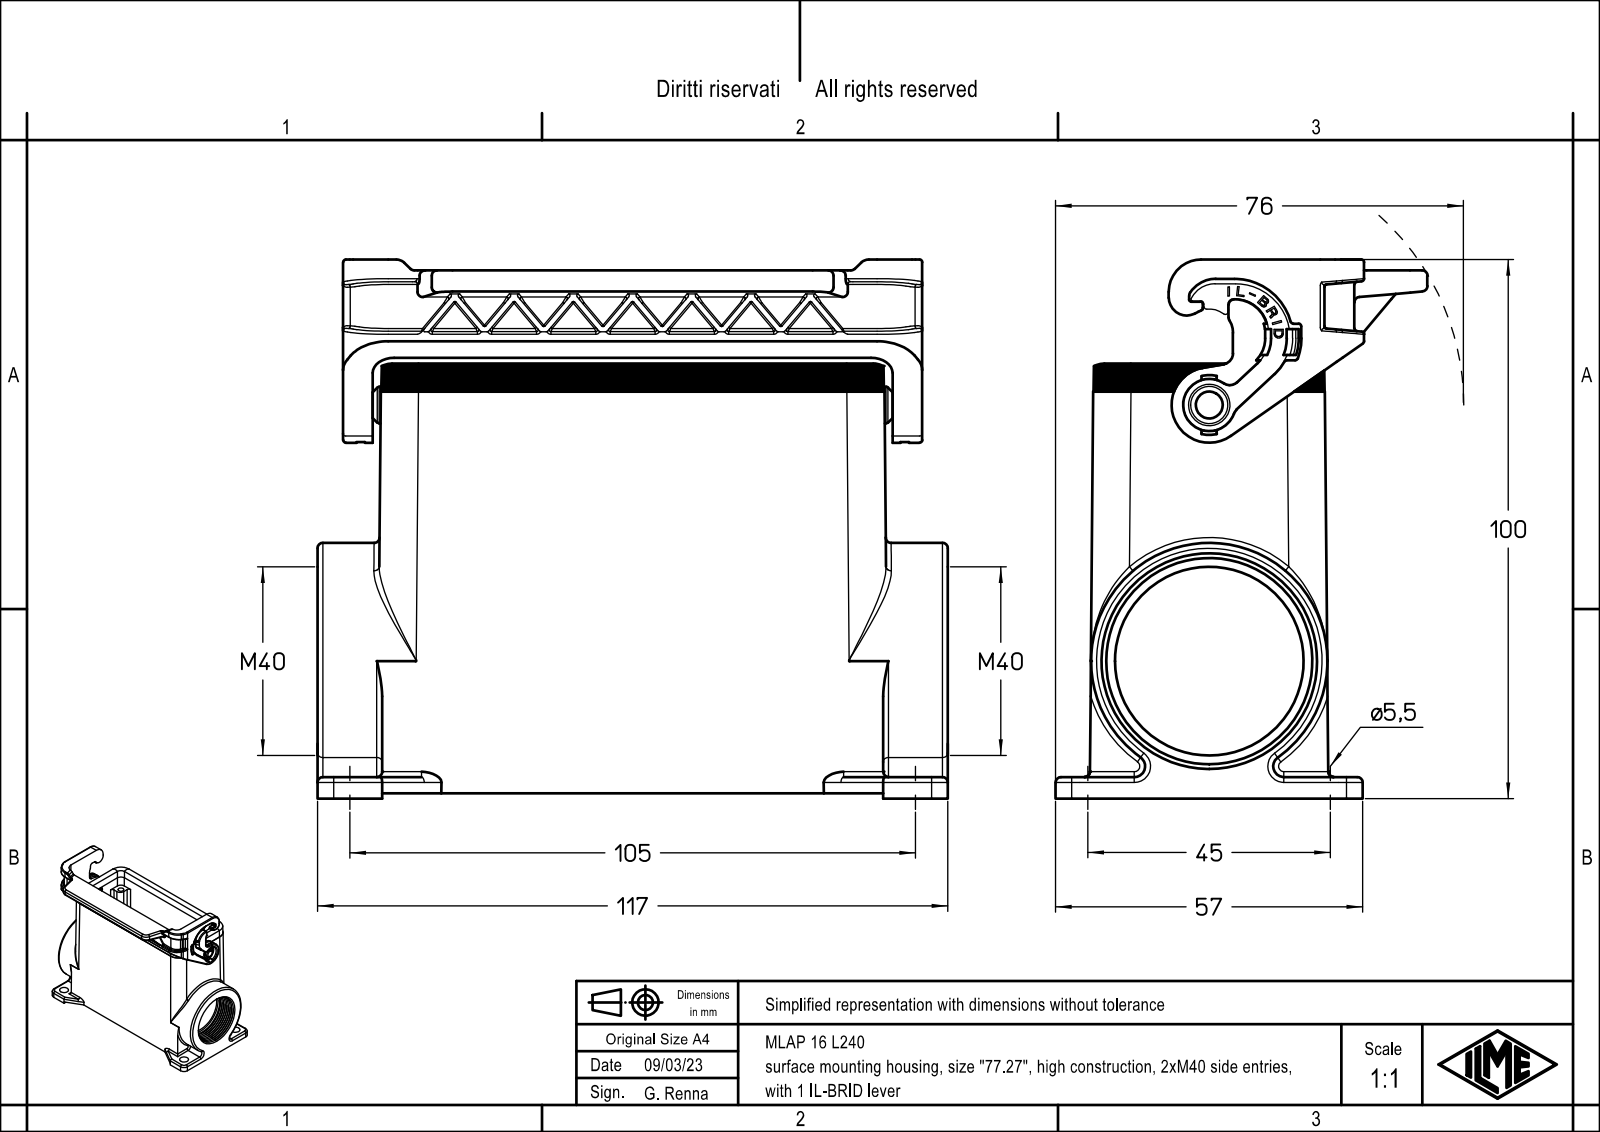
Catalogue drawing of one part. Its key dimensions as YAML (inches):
part_name: "MLAP 16 L232; MLAP 16 L240"
step_written_by: "Creo Elements/Direct Modeling 20.1B 02-Apr-2019 (C) Parametric Technology GmbH (AUTOMOTIVE_DESIGN)"
units: inches
bodies: {solids: 1, faces: 1026, planar: 639, cylindrical: 289, other: 98}
overall_size: [4.606, 3.937, 2.717]
volume: 8.007
surface_area: 105.2
round_holes:
  - {diameter: 0.118, count: 4}
  - {diameter: 0.138, count: 4}
  - {diameter: 0.217, count: 3}
  - {diameter: 0.128, count: 1}
  - {diameter: 0.213, count: 1}
  - {diameter: 0.303, count: 1}
  - {diameter: 1.26, count: 1}
  - {diameter: 1.516, count: 1}
round_bosses_or_shafts:
  - {diameter: 1.727, count: 1}
  - {diameter: 0.272, count: 1}
  - {diameter: 0.268, count: 1}
  - {diameter: 0.205, count: 1}
  - {diameter: 0.126, count: 1}
partial_cylinders:
  - {radius: 0.004, count: 27}
  - {radius: 0.118, count: 16}
  - {radius: 0.008, count: 15}
  - {radius: 0.039, count: 15}
  - {radius: 0.02, count: 11}
  - {radius: 0.079, count: 11}
  - {radius: 0.276, count: 10}
  - {radius: 0.059, count: 9}
face_to_face_distances: [0.118, 0.039, 3.819, 3.701, 0.157, 0.276, 4.016, 3.858, 0.404, 4.203]
hole_center_spacings: [0.647, 1.517, 3.61, 3.862, 1.063, 3.051, 3.231, 1.772]
